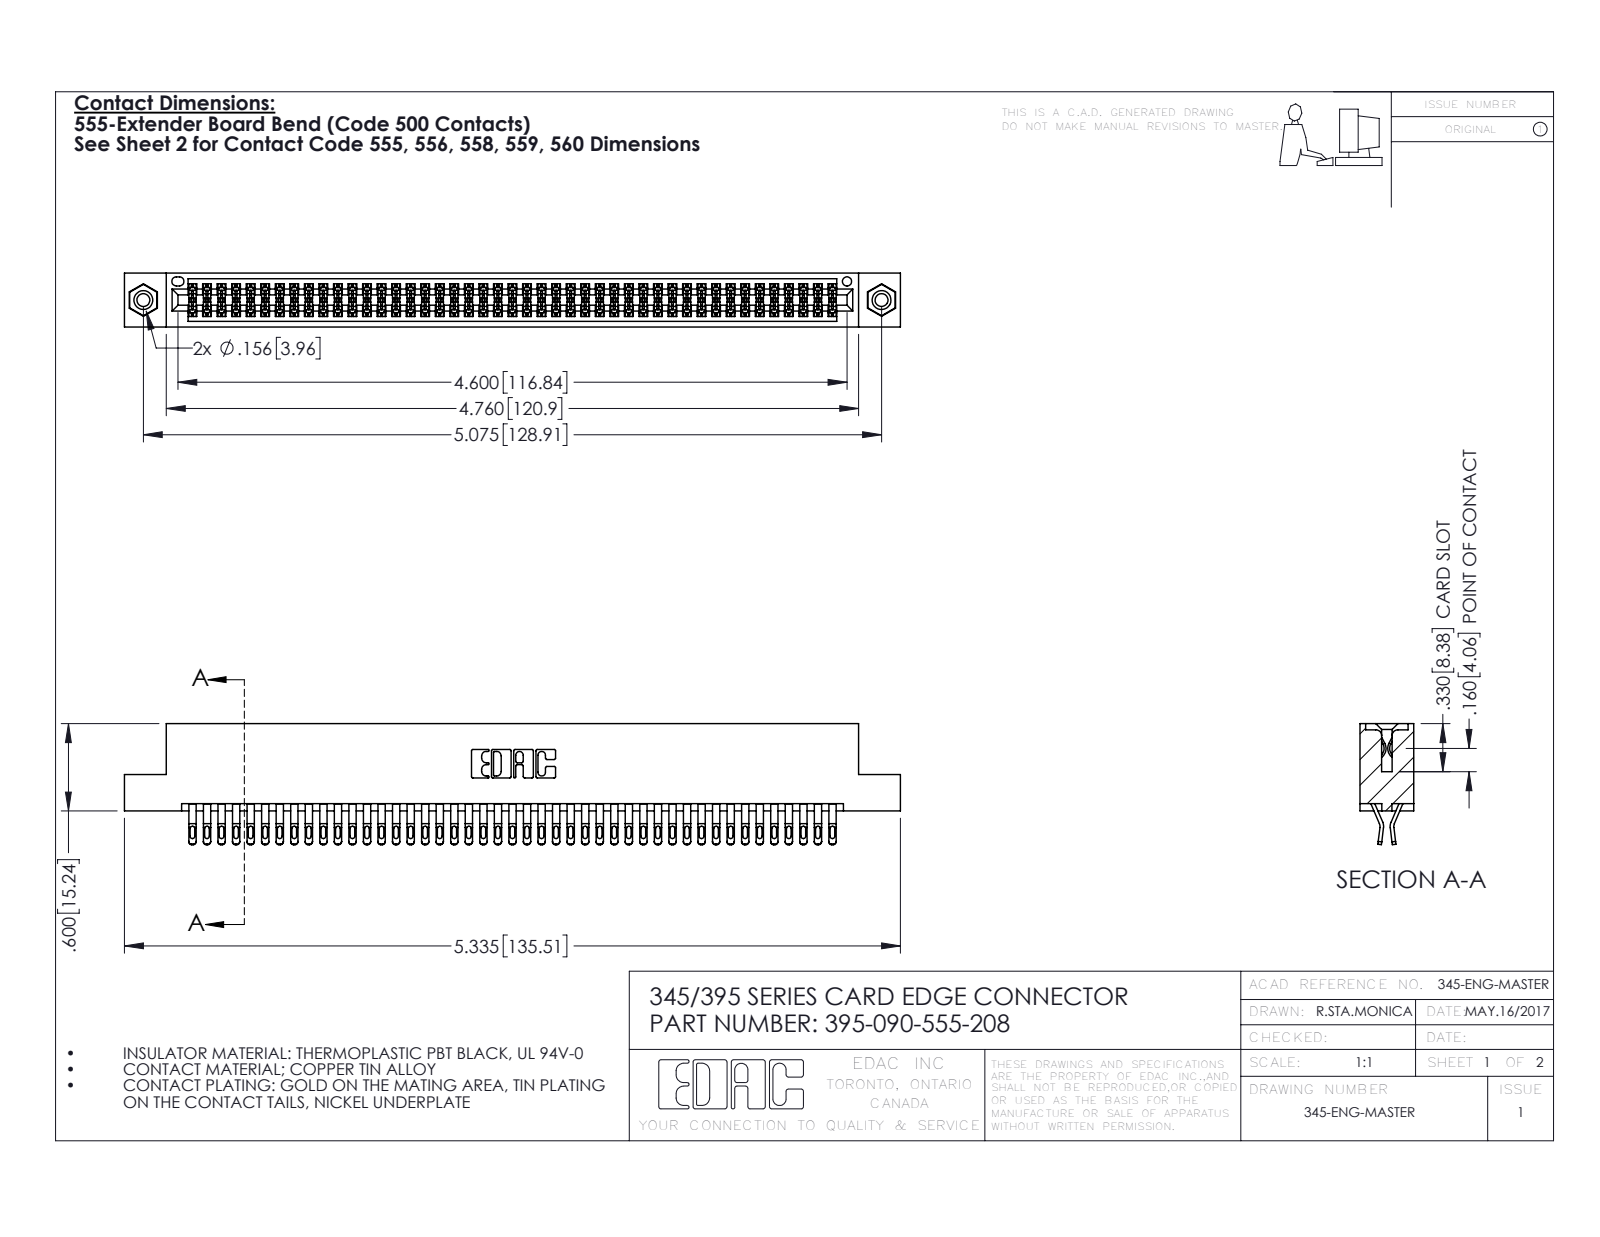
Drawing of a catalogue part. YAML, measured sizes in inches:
part_name: "345-292-001_555 Tail; 345-250-001_345-250-003-102; 345 Part_Flush Mounting Lugs - 0.156 Dia-TI; 395-090-555-208"
step_written_by: "SolidWorks 2016 (CONFIG_CONTROL_DESIGN)"
units: inches
bodies: {solids: 93, faces: 5226, planar: 2902, cylindrical: 2308, other: 16}
overall_size: [5.335, 0.832, 0.37]
volume: 0.821
surface_area: 32.32
round_holes:
  - {diameter: 0.089, count: 2}
  - {diameter: 0.125, count: 2}
  - {diameter: 0.156, count: 2}
  - {diameter: 0.064, count: 1}
round_bosses_or_shafts:
  - {diameter: 0.155, count: 2}
partial_cylinders:
  - {radius: 0.016, count: 225}
  - {radius: 0.02, count: 180}
  - {radius: 0.006, count: 135}
  - {radius: 0.01, count: 22}
  - {radius: 0.007, count: 6}
  - {radius: 0.031, count: 6}
  - {radius: 0.026, count: 3}
  - {radius: 0.01, count: 2}
face_to_face_distances: [0.072, 0.298, 0.025, 0.2, 0.37, 0.098, 0.272, 0.225, 0.175, 0.149]
hole_center_spacings: [0.27, 4.839, 5.075]
